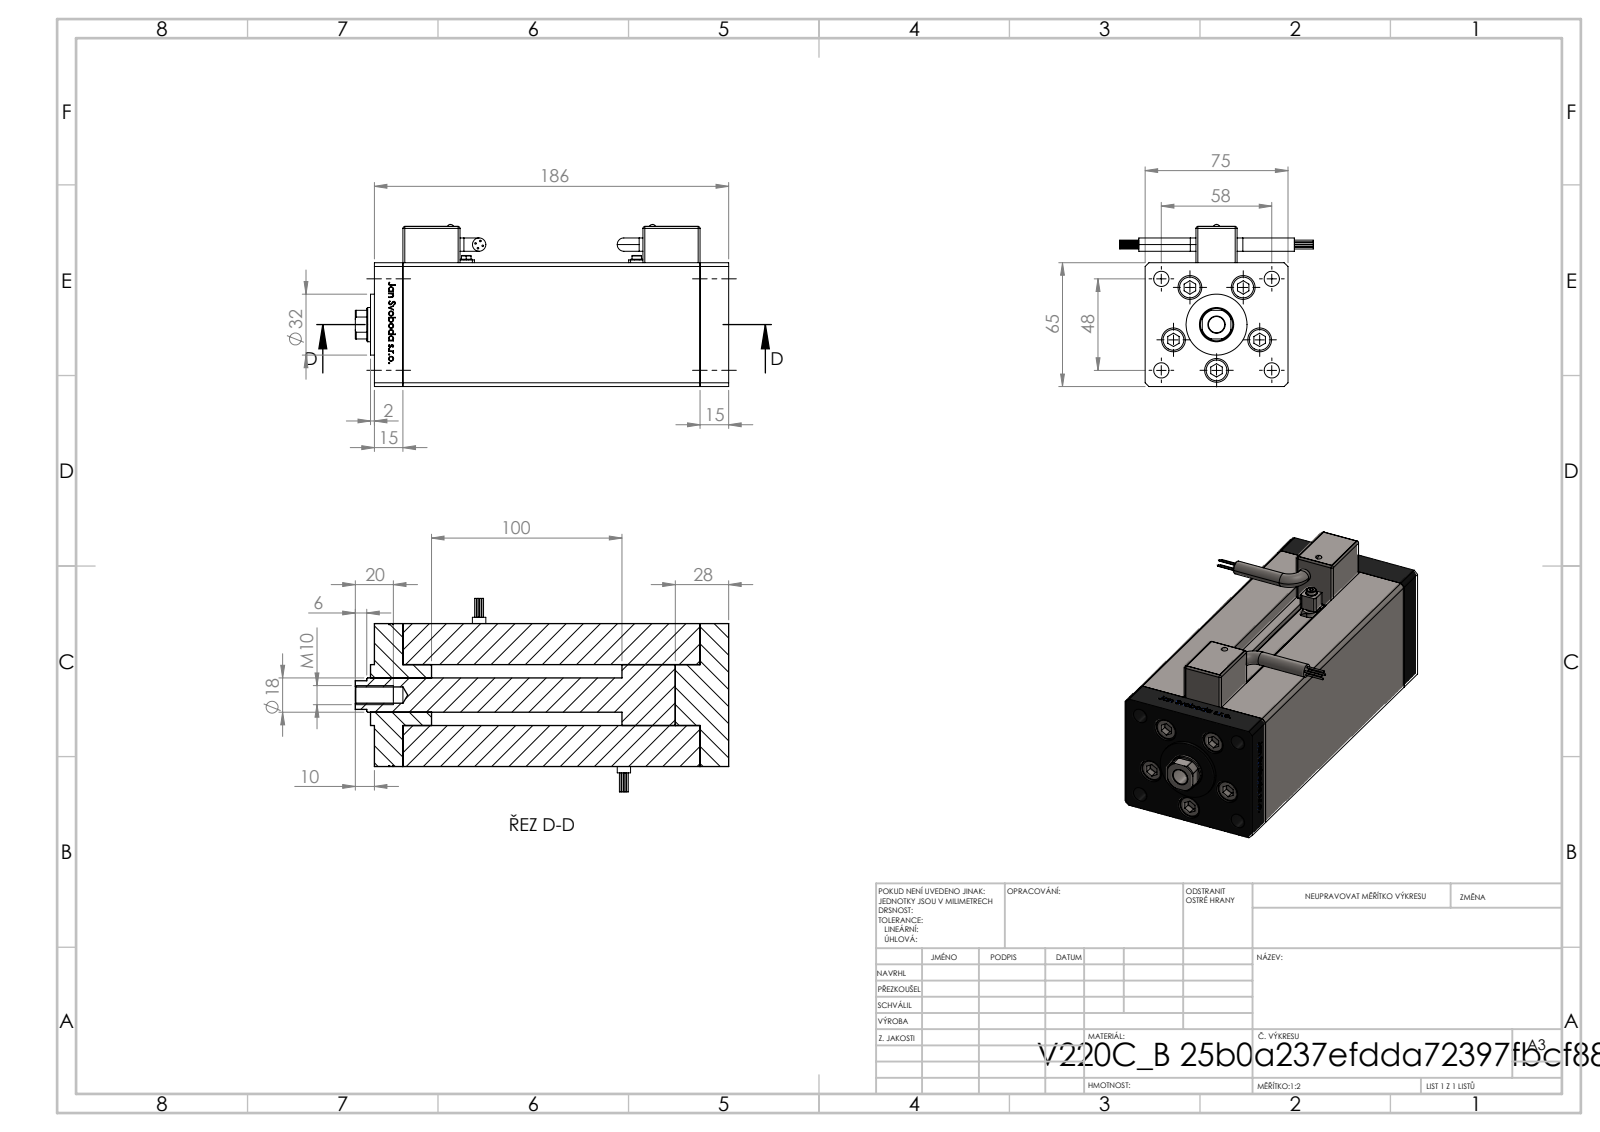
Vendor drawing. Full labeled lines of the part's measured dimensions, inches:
Part name (STEP PRODUCT): Magnetic_Switch_MSU4; V220C_B MIDDLE; V220C_VC_B; V220C BACK_B (+2 more)
STEP written by: SolidWorks 2019 (CONFIG_CONTROL_DESIGN)
Units: inches
Bodies: 16 solids, 1387 faces (540 planar, 237 cylindrical, 610 other)
Overall size (bounding box): 7.717 × 4 × 3.35
Volume: 51.42 in³ · Surface area: 229.1 in²
Round holes (diameter × count): ⌀0.354 ×5, ⌀0.492 ×5, ⌀0.315 ×4, ⌀0.079 ×2, ⌀0.142 ×2, ⌀0.197 ×2, ⌀0.276 ×2, ⌀0.518 ×2, ⌀0.335 ×1, ⌀0.709 ×1
Round bosses / shafts (diameter × count): ⌀0.033 ×8, ⌀0.315 ×5, ⌀0.276 ×4, ⌀0.236 ×2, ⌀0.138 ×2, ⌀0.098 ×2, ⌀1.26 ×1
Partial cylindrical surfaces — rounded edges, fillets, slot ends (radius × count): R0.039 ×24, R0.157 ×4, R0.037 ×2, R0.335 ×1
Main face-to-face distances: 2.953, 2.559, 0.591, 6.142, 6.732, 7.323, 2.303, 0.256, 1.902, 1.051
Hole centre spacings: 0.945, 1.482, 0.325, 0.617, 0.678, 1.091, 1.135, 1.142
